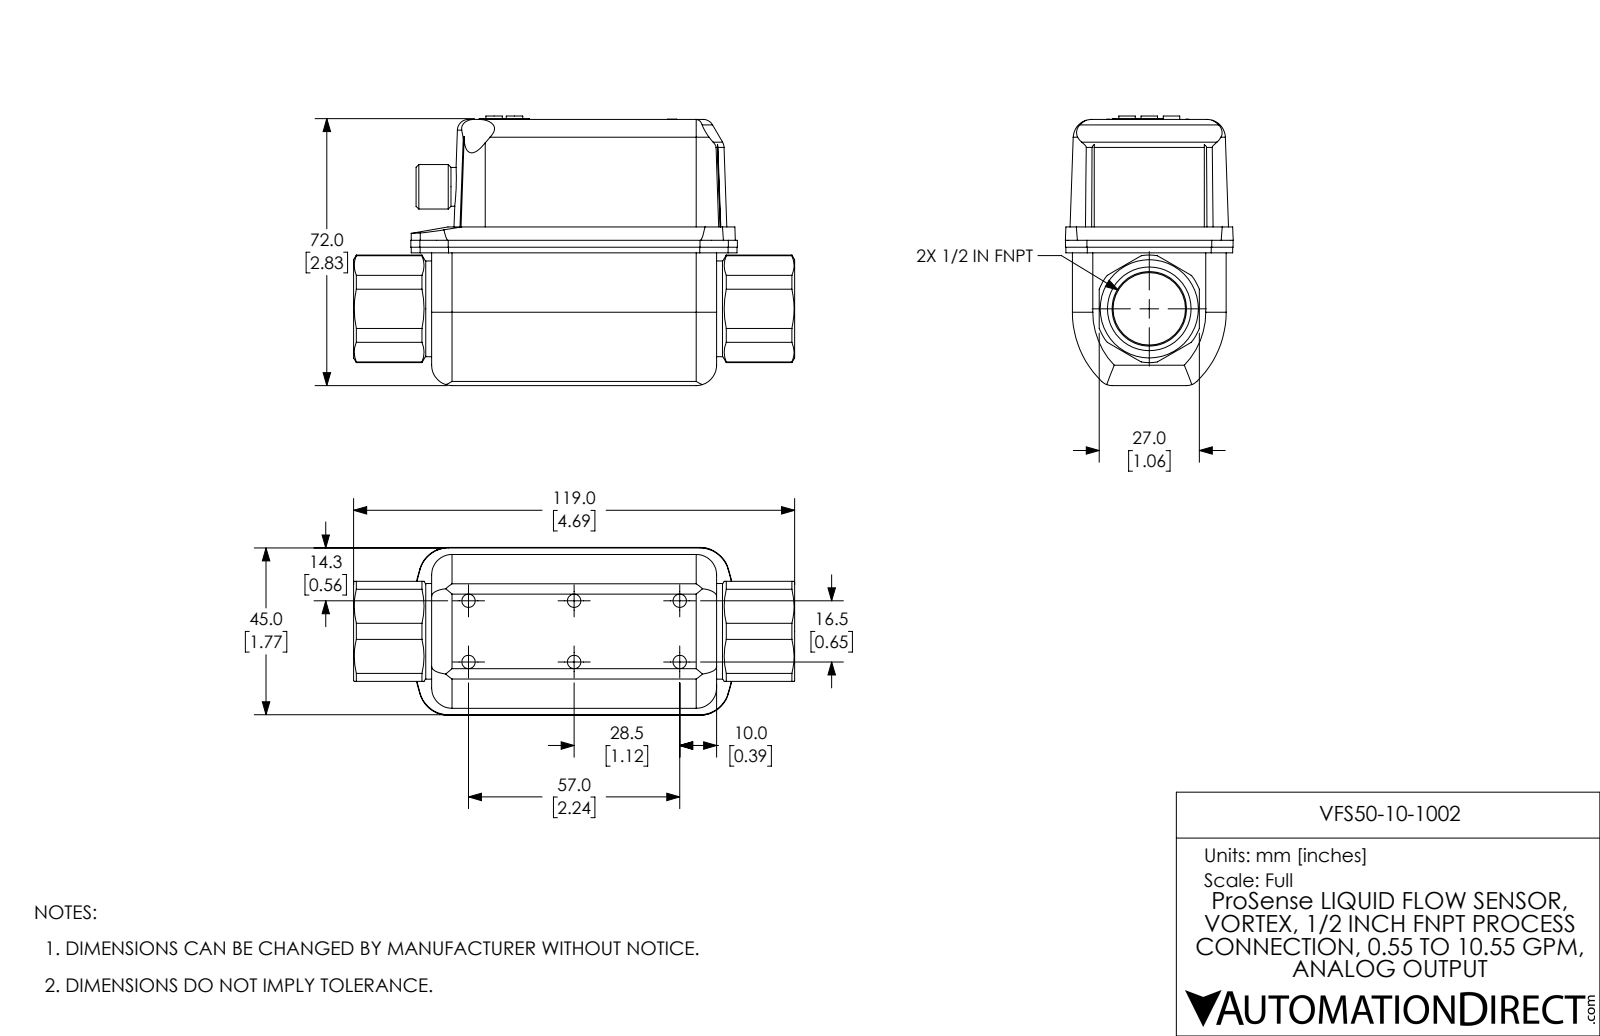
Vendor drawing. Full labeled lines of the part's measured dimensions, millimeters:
Part name (STEP PRODUCT): VFS50-10-1002
STEP written by: SolidWorks 2017 (AUTOMOTIVE_DESIGN)
Units: millimetres
Bodies: 1 solid, 219 faces (84 planar, 80 cylindrical, 55 other)
Overall size (bounding box): 119 × 72.7 × 45.29
Volume: 234 166 mm³ · Surface area: 27 599 mm²
Round holes (diameter × count): ⌀3.6 ×6, ⌀8.4 ×1
Round bosses / shafts (diameter × count): ⌀4.45 ×3, ⌀25.8 ×1, ⌀12 ×1, ⌀10.5 ×1
Partial cylindrical surfaces — rounded edges, fillets, slot ends (radius × count): R8 ×12, R5.5 ×6, R4 ×4, R60 ×4, R3.5 ×2, R5 ×2, R26 ×2, R0.6 ×1
Main face-to-face distances: 27, 71.8, 41.5, 36, 7.25, 34.25, 71.75, 35.8, 35.95, 11.05
Hole centre spacings: 28.5, 32.93, 16.5, 57, 59.34
